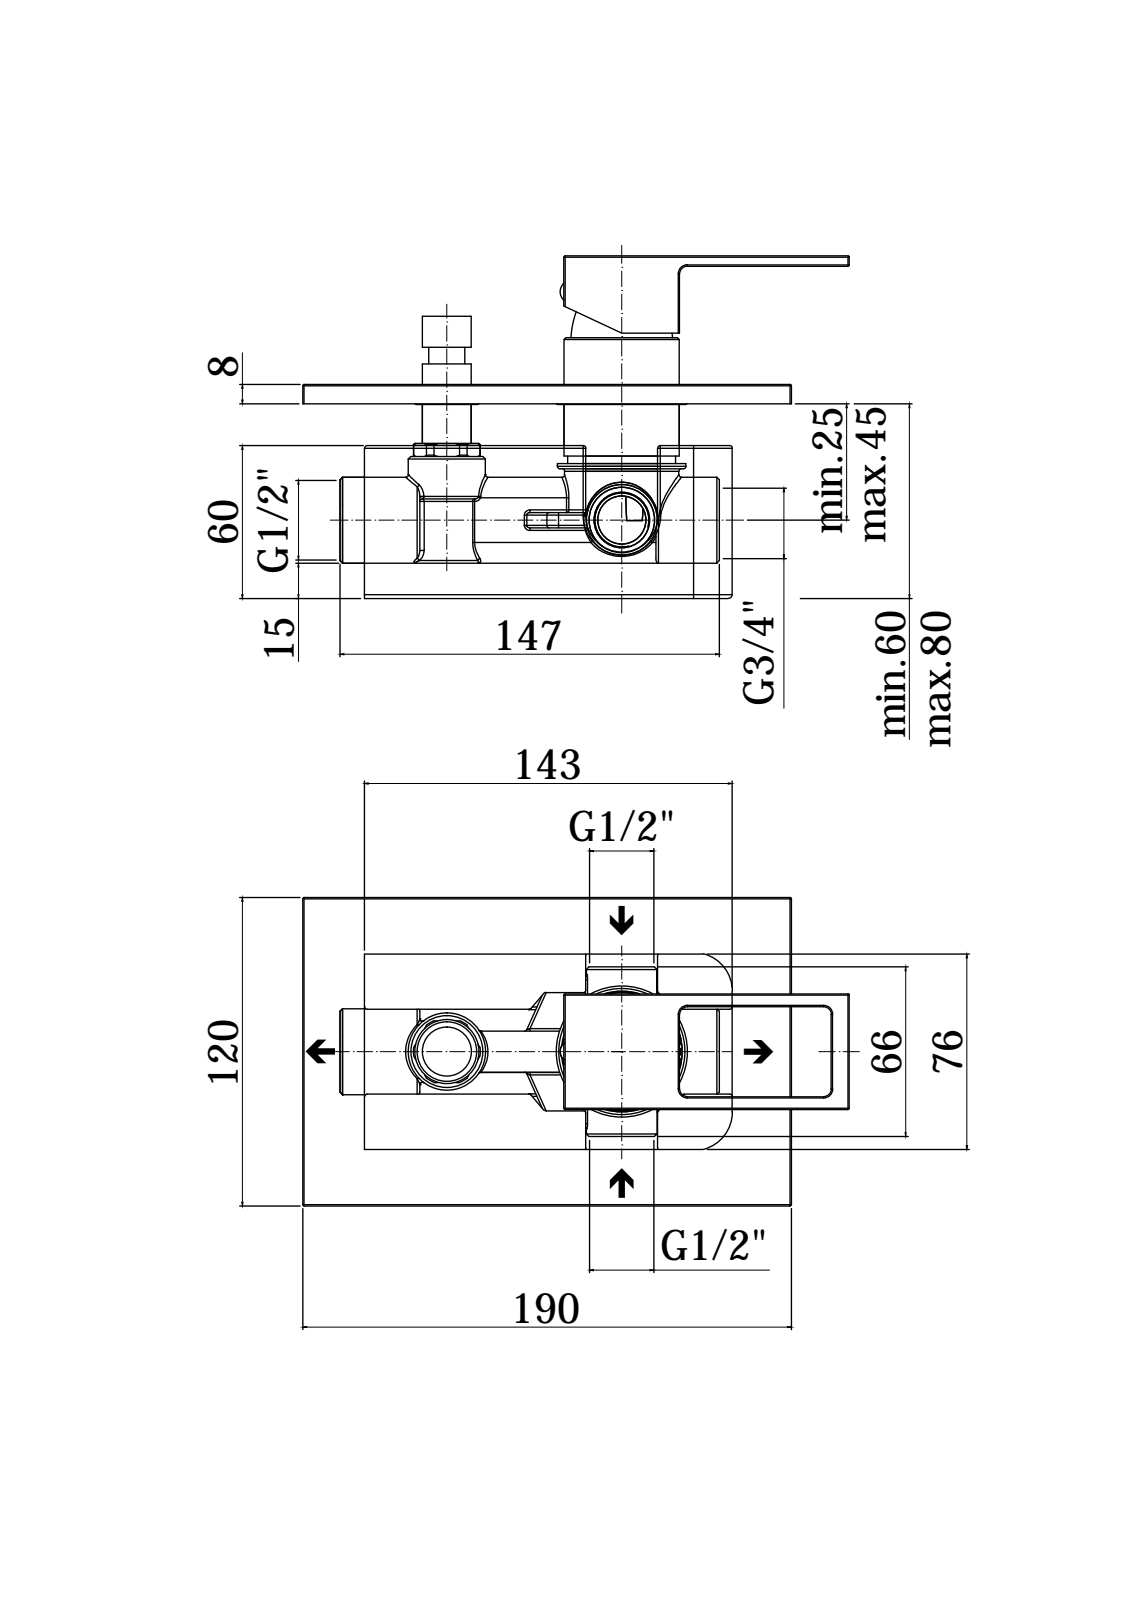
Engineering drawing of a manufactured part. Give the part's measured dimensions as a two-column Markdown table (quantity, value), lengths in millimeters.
| quantity | value |
| --- | --- |
| part name | EF015CR |
| STEP written by | CREO PARAMETRIC BY PTC INC, 2020044 (CONFIG_CONTROL_DESIGN) |
| units | millimeters |
| bodies | 5 solids, 1033 faces (607 planar, 259 cylindrical, 167 other) |
| overall size | 212.5 × 120 × 59.6 |
| volume | 171 773 mm³ |
| surface area | 100 084 mm² |
| round holes (diameter × count) | 4 × 2, 3 × 1, 4.5 × 1, 5 × 1, 5.5 × 1, 7.8 × 1, 10.5 × 1, 14.8 × 1, 19.2 × 1, 19.5 × 1, 19.9 × 1, 20 × 1 |
| round bosses / shafts (diameter × count) | 51 × 1, 49 × 1, 44.8 × 1, 35 × 1, 32.2 × 1, 25 × 1, 23.5 × 1, 23.4 × 1 |
| partial cylindrical surfaces (radius × count) | 0.5 × 51, 0.15 × 11, 1 × 10, 3 × 5, 0.3 × 4, 4 × 1, 7 × 1, 9.3 × 1 |
| main face-to-face distances | 8, 2.5, 5.5, 22.5, 37.5, 82.5, 59.6, 54.1, 51.6, 45 |
| hole center spacings | 9.5, 68 |
